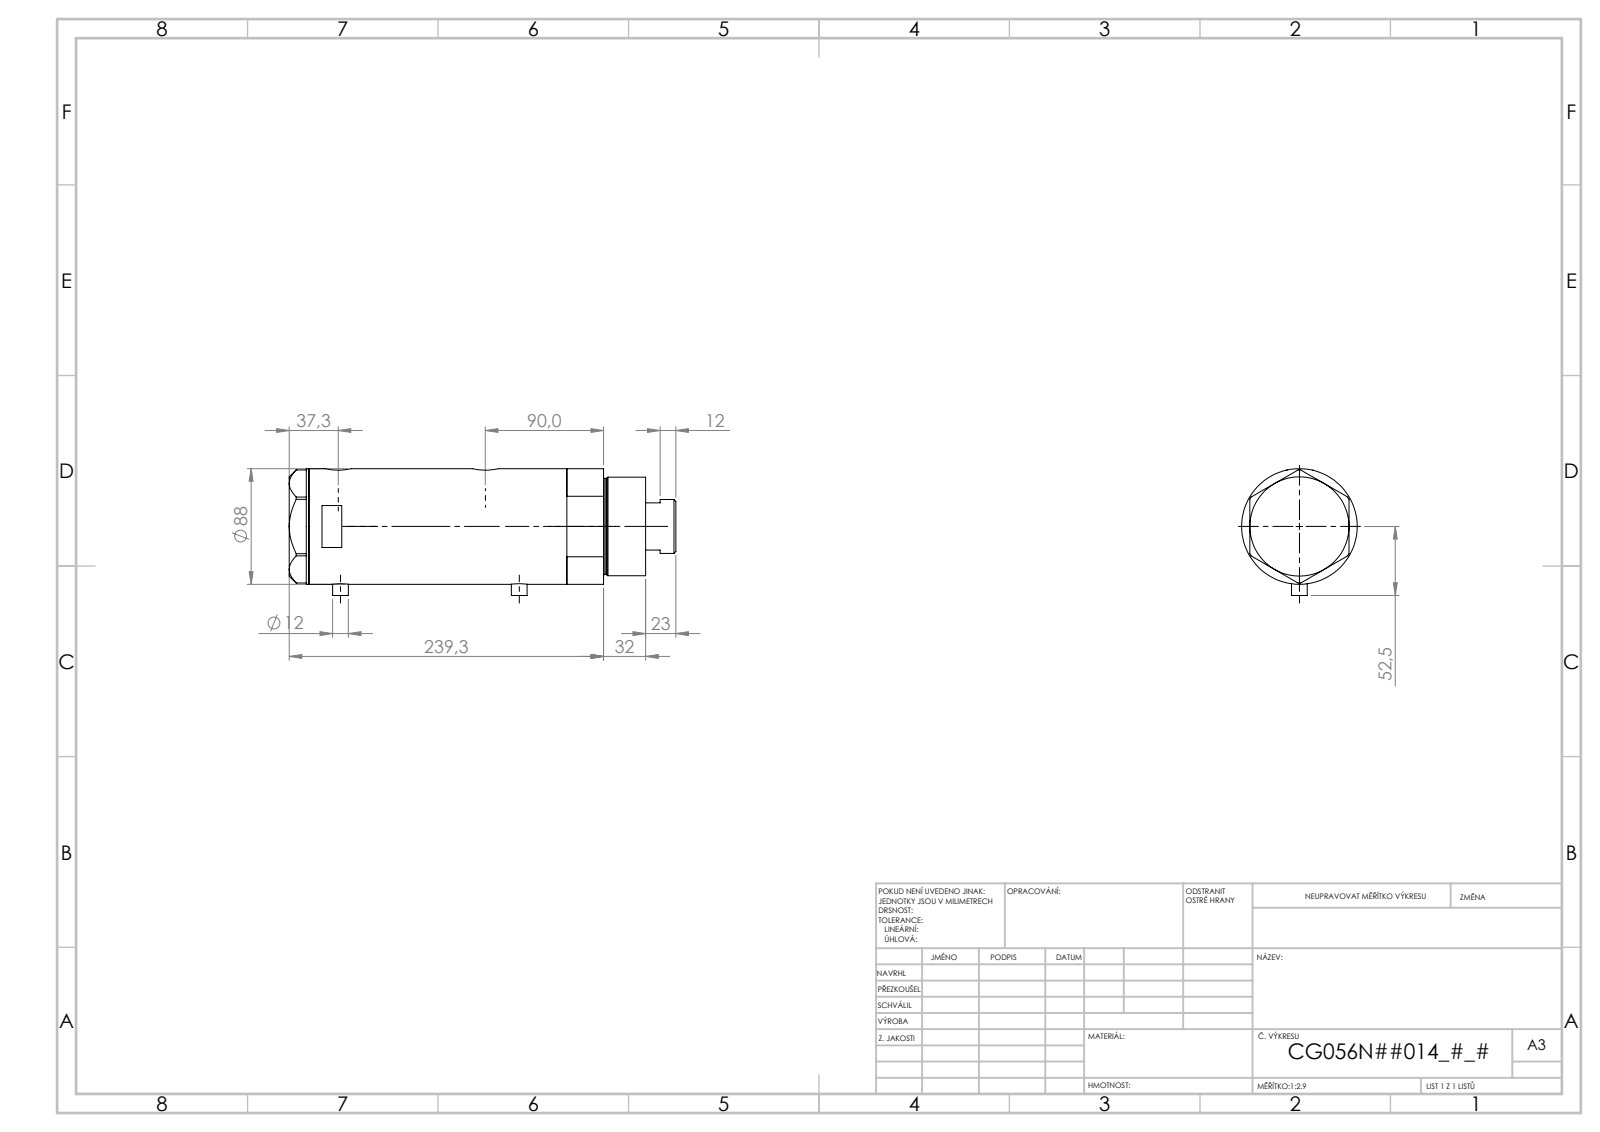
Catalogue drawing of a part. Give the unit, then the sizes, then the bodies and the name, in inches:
Units: inches
Overall size (bounding box): 11.587 × 3.799 × 3.465
Round holes (diameter × count): ⌀0.492 ×2, ⌀0.518 ×2, ⌀0.787 ×2, ⌀0.571 ×1, ⌀1.654 ×1, ⌀1.713 ×1, ⌀2.205 ×1, ⌀2.362 ×1, ⌀3.15 ×1
Round bosses / shafts (diameter × count): ⌀0.472 ×2, ⌀3.465 ×1, ⌀2.953 ×1, ⌀2.874 ×1, ⌀1.614 ×1
Main face-to-face distances: 5.291, 1.024, 4.268, 0.591, 1.614, 5.882, 10.091, 10.681, 9.067, 4.799
Hole centre spacings: 0.067, 1.016, 4.343, 4.409, 5.358, 5.425
Volume: 95.99 in³ · Surface area: 345.7 in²
Bodies: 4 solids, 121 faces (52 planar, 49 cylindrical, 20 other)
Part name (STEP PRODUCT): V270CG_BACK; V270CG_MIDDLE; V270CG_VC; V270CG_FRONT
STEP written by: SolidWorks 2019 (CONFIG_CONTROL_DESIGN)
